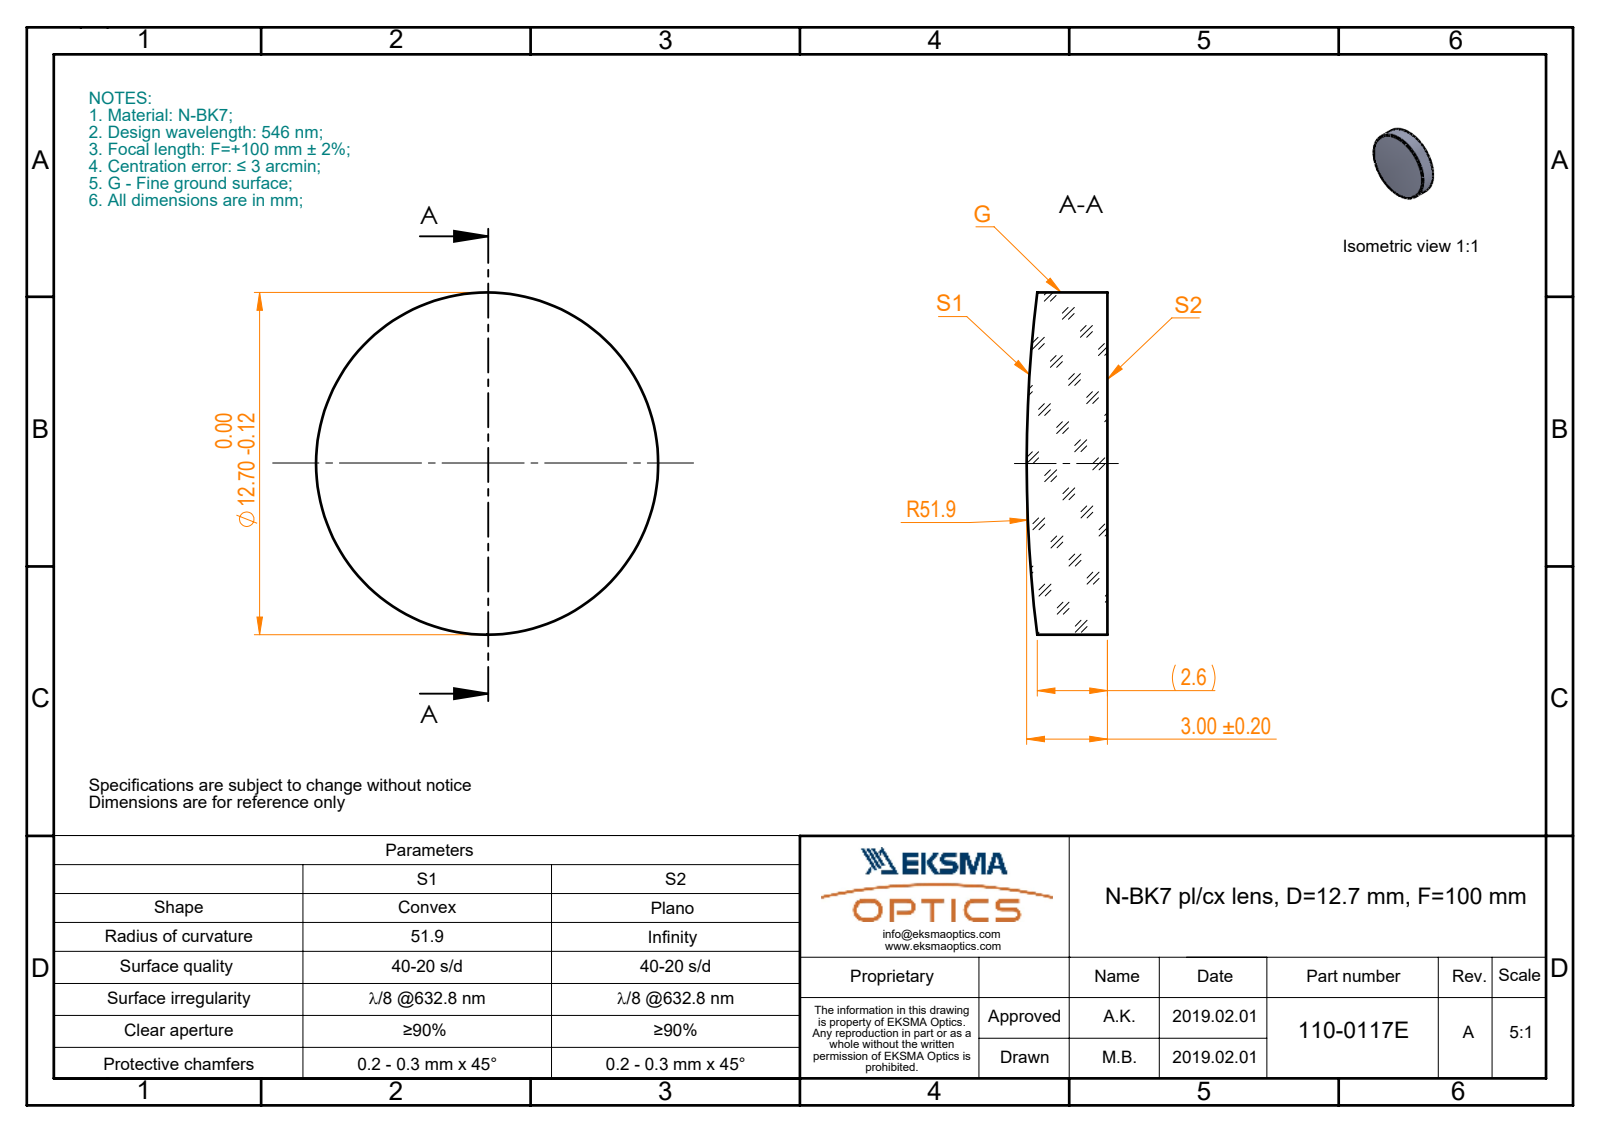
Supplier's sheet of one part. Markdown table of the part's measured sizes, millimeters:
| quantity | value |
| --- | --- |
| part name | 110-0117E BK7 pl-cx 12.7 F100 |
| STEP written by | SolidWorks 2017 (CONFIG_CONTROL_DESIGN) |
| units | millimeters |
| bodies | 1 solid, 5 faces (1 planar, 2 cylindrical, 2 other) |
| overall size | 12.7 × 12.7 × 3 |
| volume | 355 mm³ |
| surface area | 358 mm² |
| round bosses / shafts (diameter × count) | 12.7 × 1 |
